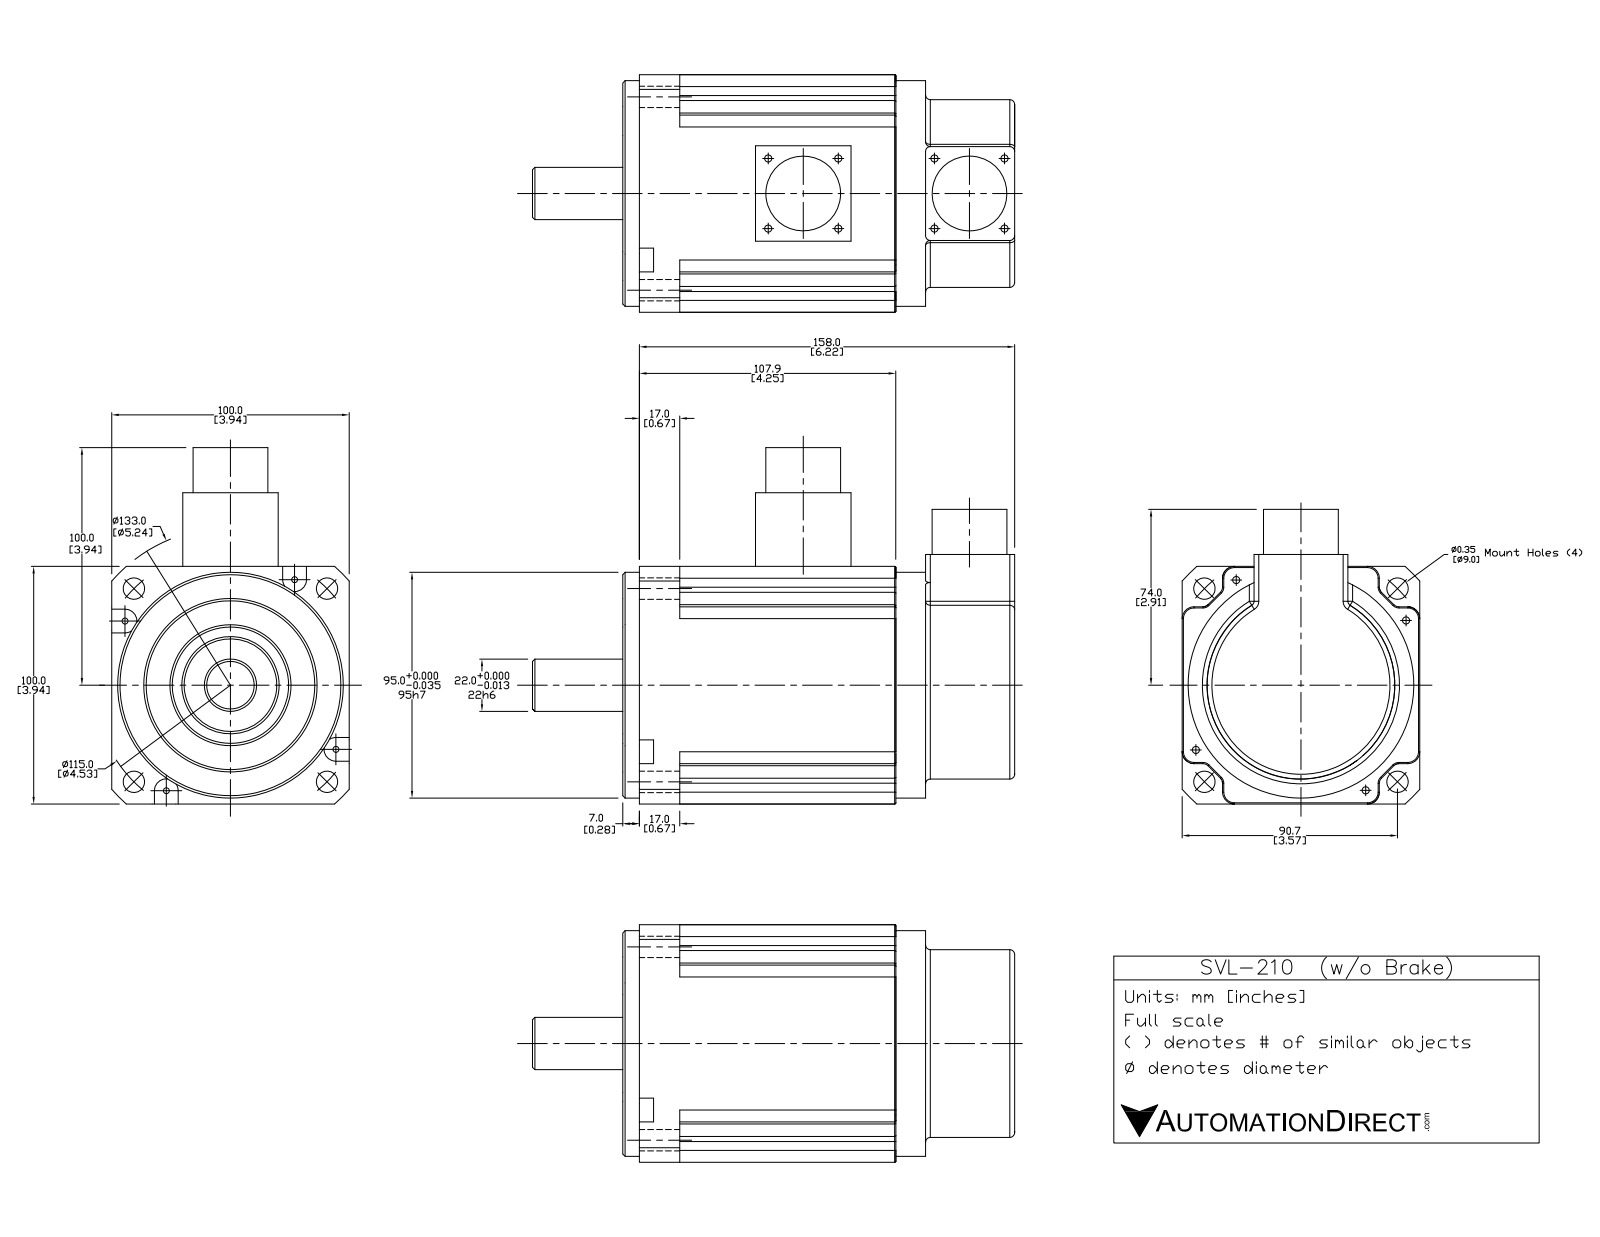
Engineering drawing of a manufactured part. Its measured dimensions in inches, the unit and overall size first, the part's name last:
Units: inches
Overall size (bounding box): 7.992 × 5.906 × 3.937
Round holes (diameter × count): ⌀0.354 ×4, ⌀1.063 ×1, ⌀1.071 ×1, ⌀2.835 ×1
Round bosses / shafts (diameter × count): ⌀0.079 ×17, ⌀0.315 ×8, ⌀0.059 ×6, ⌀0.098 ×3, ⌀1.24 ×2, ⌀3.74 ×1, ⌀3.268 ×1, ⌀1.969 ×1
Partial cylindrical surfaces — rounded edges, fillets, slot ends (radius × count): R0.197 ×20, R0.079 ×4, R0.157 ×4, R2.618 ×1
Main face-to-face distances: 3.091, 3.937, 0.276, 3.839, 1.024, 4.114, 0.748, 2.382, 5.472, 6.22
Hole centre spacings: 2.264, 3.202, 4.528, 2.691
Volume: 84.46 in³ · Surface area: 210.9 in²
Bodies: 36 solids, 433 faces (186 planar, 166 cylindrical, 81 other)
Part name (STEP PRODUCT): SVL-210
STEP written by: SolidWorks 2015 (AUTOMOTIVE_DESIGN)
